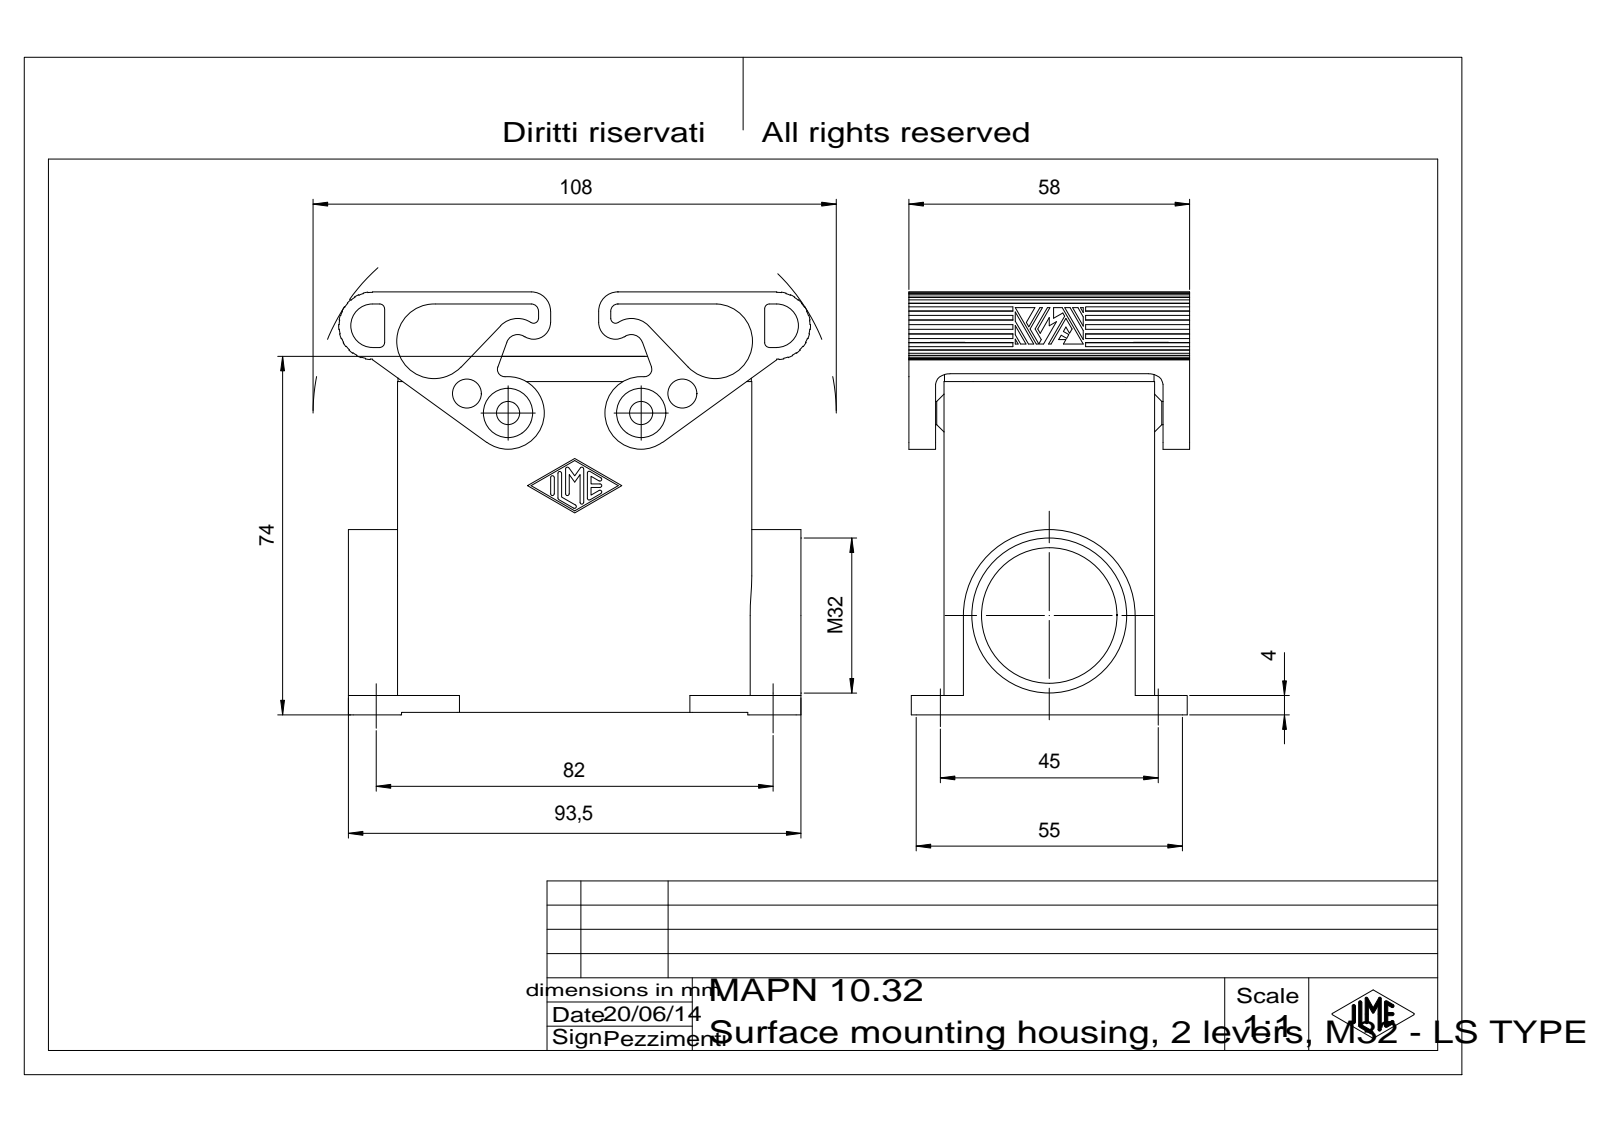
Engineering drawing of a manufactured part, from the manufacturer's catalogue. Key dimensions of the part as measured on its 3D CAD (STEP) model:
Part name (STEP PRODUCT): MAPN_10.32
STEP written by: CoCreate Modeling 16.00A 16-Aug-2008 (C) Parametric Technology GmbH (AUTOMOTIVE_DESIGN)
Units: millimetres
Bodies: 0 solids, 918 faces (436 planar, 372 cylindrical, 110 other)
Overall size (bounding box): 98.1 × 87.3 × 58
Round holes (diameter × count): ⌀2.46 ×4, ⌀3.1 ×4, ⌀5.5 ×4, ⌀6 ×2, ⌀10.2 ×2, ⌀28 ×1, ⌀32 ×1
Round bosses / shafts (diameter × count): ⌀4.8 ×2
Partial cylindrical surfaces — rounded edges, fillets, slot ends (radius × count): R1 ×26, R0.8 ×16, R3 ×12, R0.9 ×8, R1.5 ×8, R6 ×8, R0.2 ×4, R0.5 ×4
Main face-to-face distances: 3, 40.5, 43.5, 4.75, 45.25, 37.5, 3.5, 1.75, 42.25, 4
Hole centre spacings: 15.4, 38.11, 70.08, 78.27, 9.39, 27, 36.22, 45
